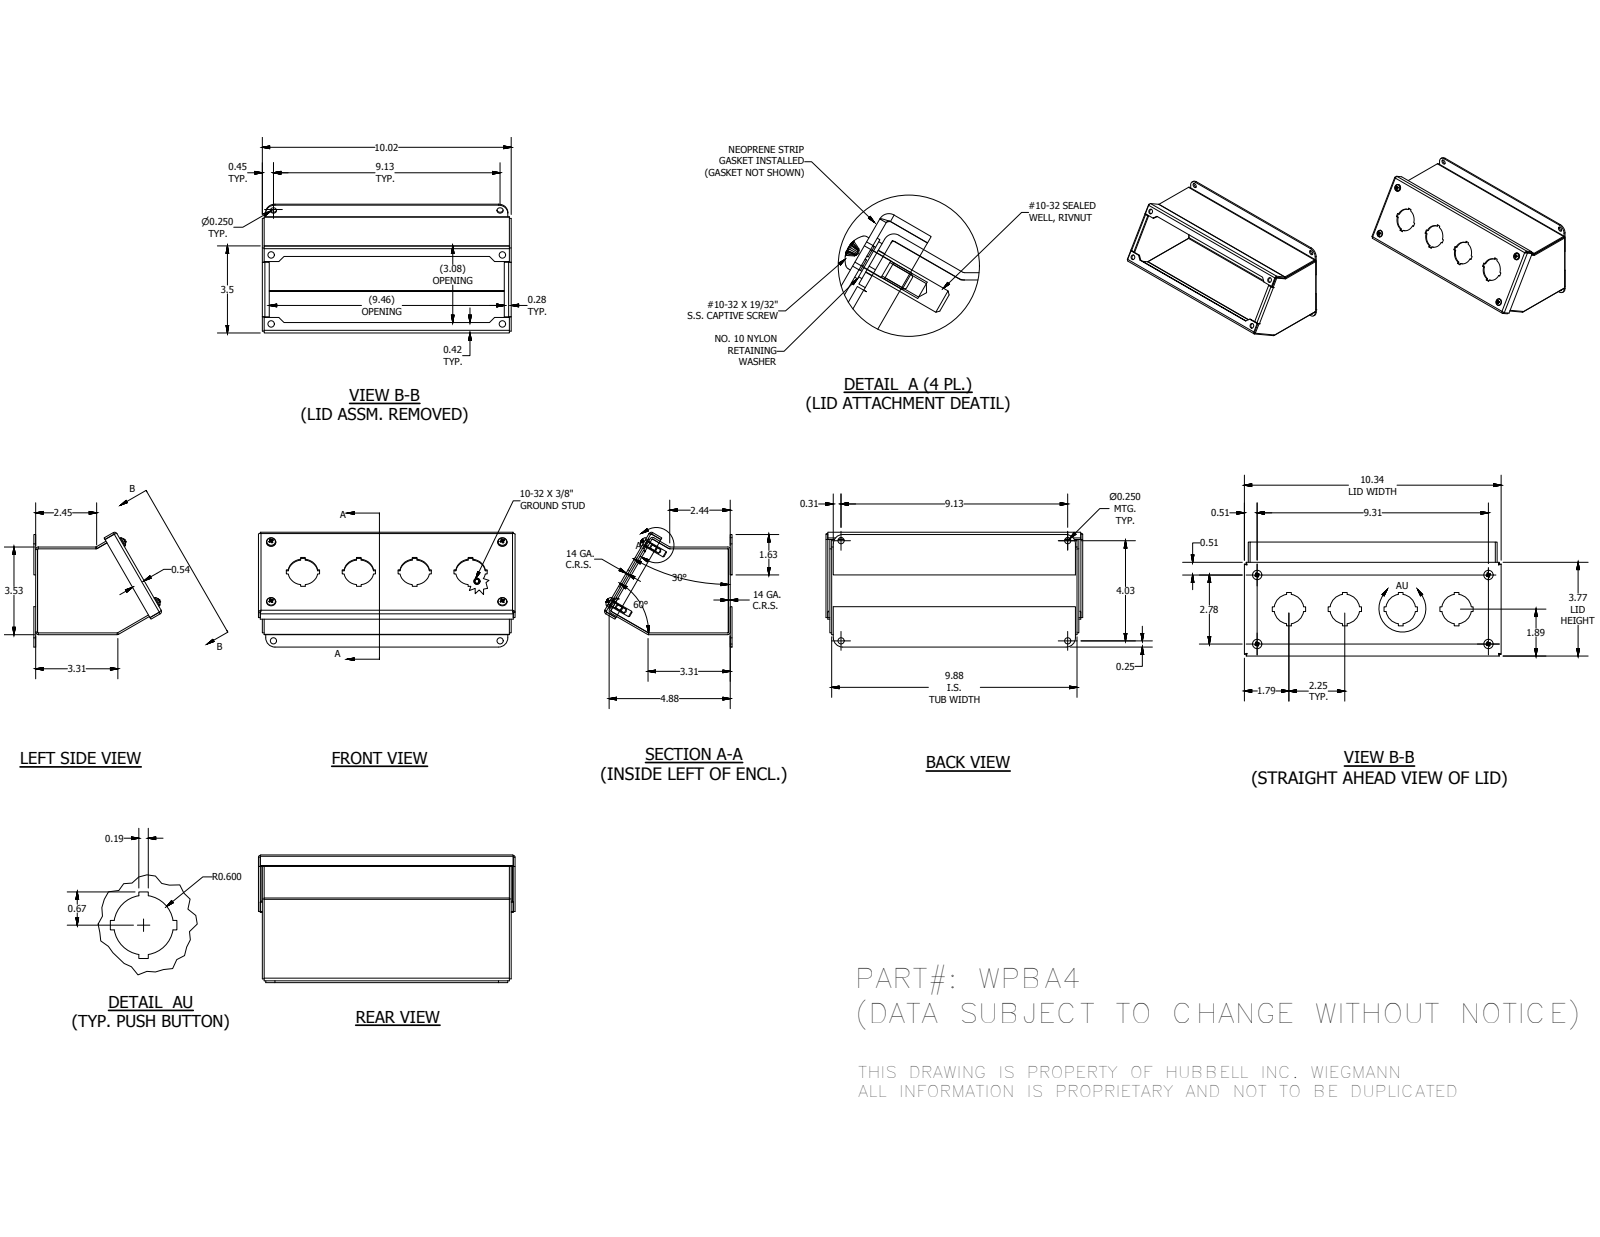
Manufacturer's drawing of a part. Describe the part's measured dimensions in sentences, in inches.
The part is named "WPBA4BKP; WPBA1ROWEWPR; WPBA1ROWEWPL; 34984 (+6 more)". Its 3-D file was written by "Autodesk Inventor 2014 (AUTOMOTIVE_DESIGN)". It is 19 solids with 528 faces: 323 planar, 106 cylindrical and 99 other. Overall it measures 10.337 by 5.141 by 4.623 inches. Its volume is 17.18 cubic inches and its surface area 480.3 square inches. Round holes: 4 of diameter 0.156, 4 of diameter 0.196, 4 of diameter 0.25, 4 of diameter 0.257, 4 of diameter 0.278, 4 of diameter 0.281, 4 of diameter 1.2. Round bosses or shafts: 5 of diameter 0.19, 4 of diameter 0.453, 4 of diameter 0.406, 4 of diameter 0.373, 4 of diameter 0.248, 1 of diameter 0.25. Partial cylindrical surfaces (rounded edges, fillets, slot ends): 12 of radius 0.031, 12 of radius 0.105, 4 of radius 0.089, 4 of radius 0.375. The main face-to-face distances are 0.074, 3.456, 0.148, 9.949, 3.382, 3.53, 3.424, 9.875, 10.023, 3.576. The hole center spacings are 2.25, 2.749, 2.777, 5.942, 9.312, 9.313, 0.028, 1.879.
